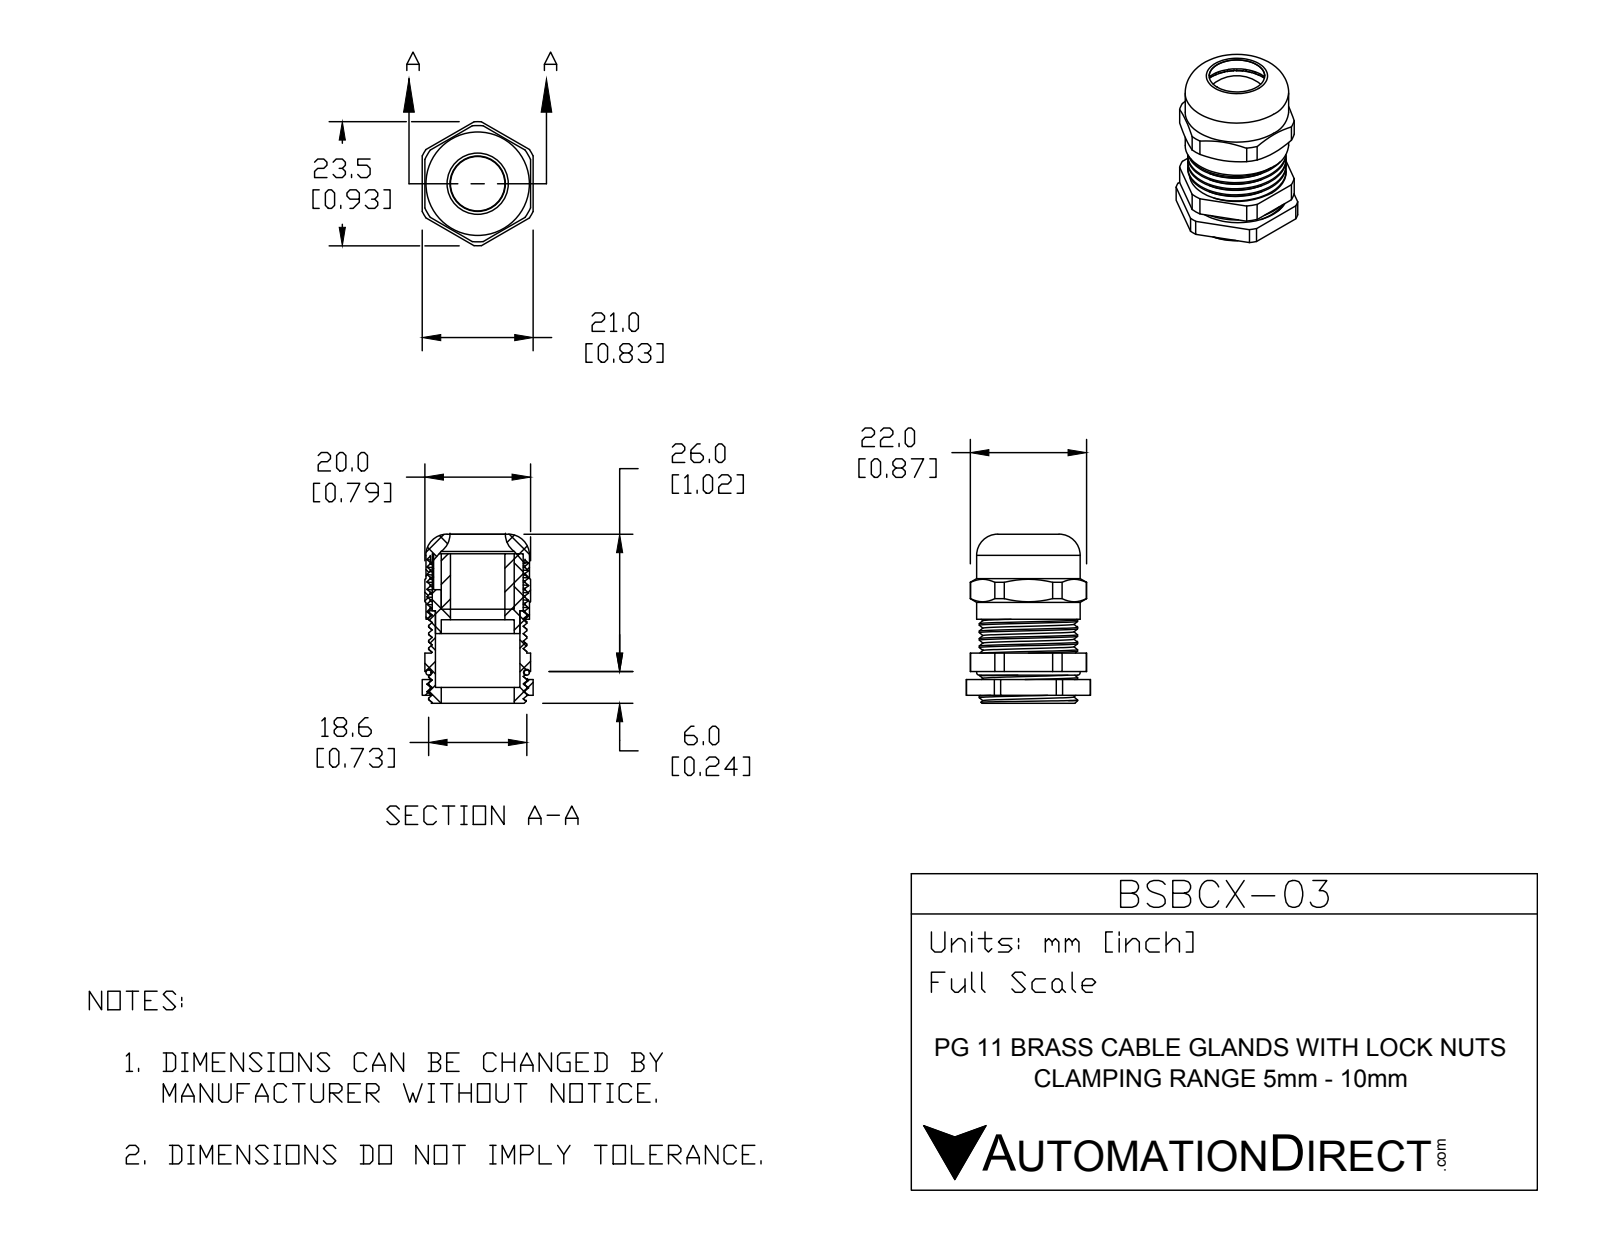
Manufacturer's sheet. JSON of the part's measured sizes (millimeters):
{"part_name": "BSBCX-03", "step_written_by": "SolidWorks 2015 (CONFIG_CONTROL_DESIGN)", "units": "millimeters", "bodies": {"solids": 6, "faces": 255, "planar": 135, "cylindrical": 86, "other": 34}, "overall_size": [32, 23.5, 21], "volume_mm3": 4754, "surface_area_mm2": 9105, "round_holes": [[10.3, 1], [10.5, 1], [13.8, 1], [16, 1], [17.93, 1]], "round_bosses_or_shafts": [[19.6, 1], [18.6, 1], [17.2, 1]], "partial_cylinders_radius": [[11, 1], [11.75, 1]], "face_to_face_distances": [0.5, 1.5, 20, 3, 20.5, 8, 10.5, 4.5, 16.3, 26.8]}
